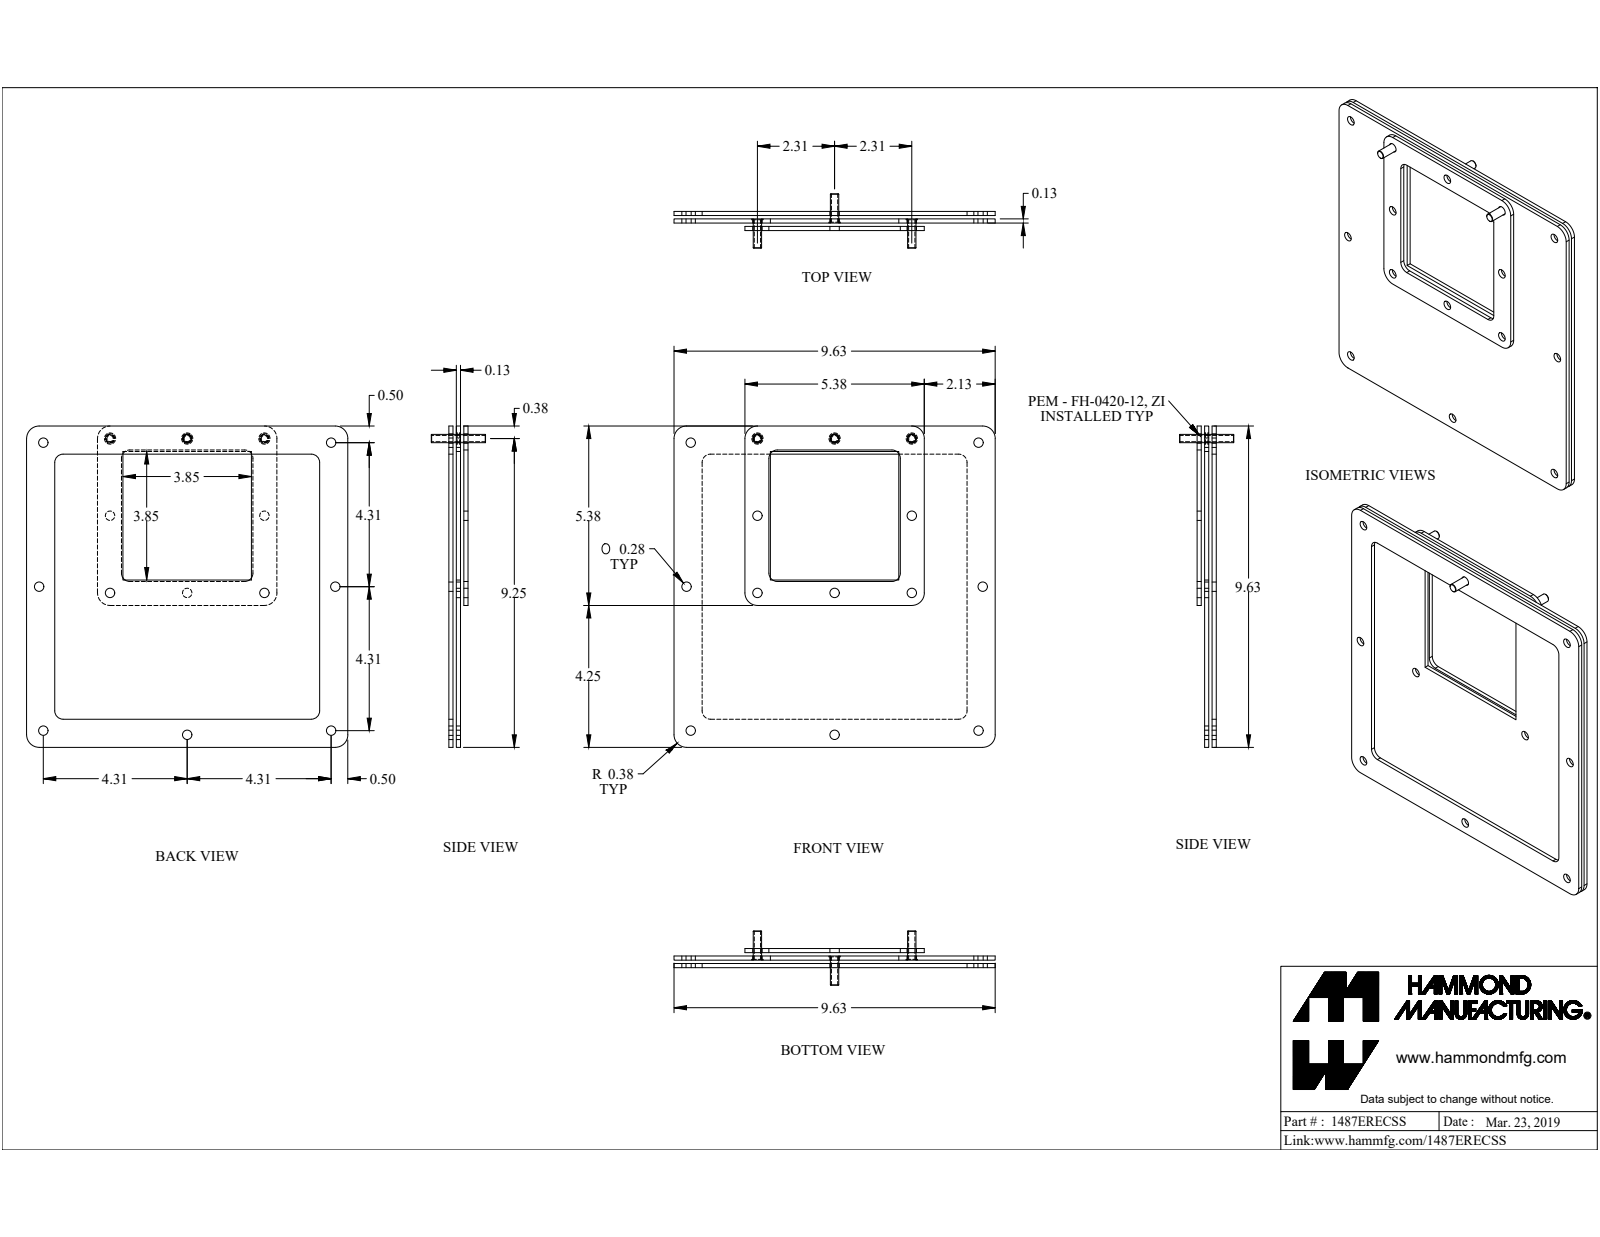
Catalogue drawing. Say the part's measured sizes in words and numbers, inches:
The part is named "1487ERECSS". Its 3-D file was written by "SolidWorks 2019 (CONFIG_CONTROL_DESIGN)". It is 12 solids with 270 faces: 153 planar, 98 cylindrical and 19 other. Overall it measures 9.625 by 9.625 by 1.625 inches. Its volume is 15.17 cubic inches and its surface area 267.8 square inches. Round holes: 15 of diameter 0.281, 3 of diameter 0.249, 2 of diameter 0.196, 2 of diameter 0.258, 2 of diameter 0.35. Round bosses or shafts: 5 of diameter 0.25, 3 of diameter 0.337, 2 of diameter 0.5. Partial cylindrical surfaces (rounded edges, fillets, slot ends): 12 of radius 0.02, 8 of radius 0.25, 8 of radius 0.375. The main face-to-face distances are 0.125, 0.225, 0.1, 0.35, 0.45, 0.225, 0.325, 0.35, 0.1, 0.575. The hole center spacings are 9.755, 4.315, 5.171, 2.313, 6.276, 4.625, 8.625, 2.312.
